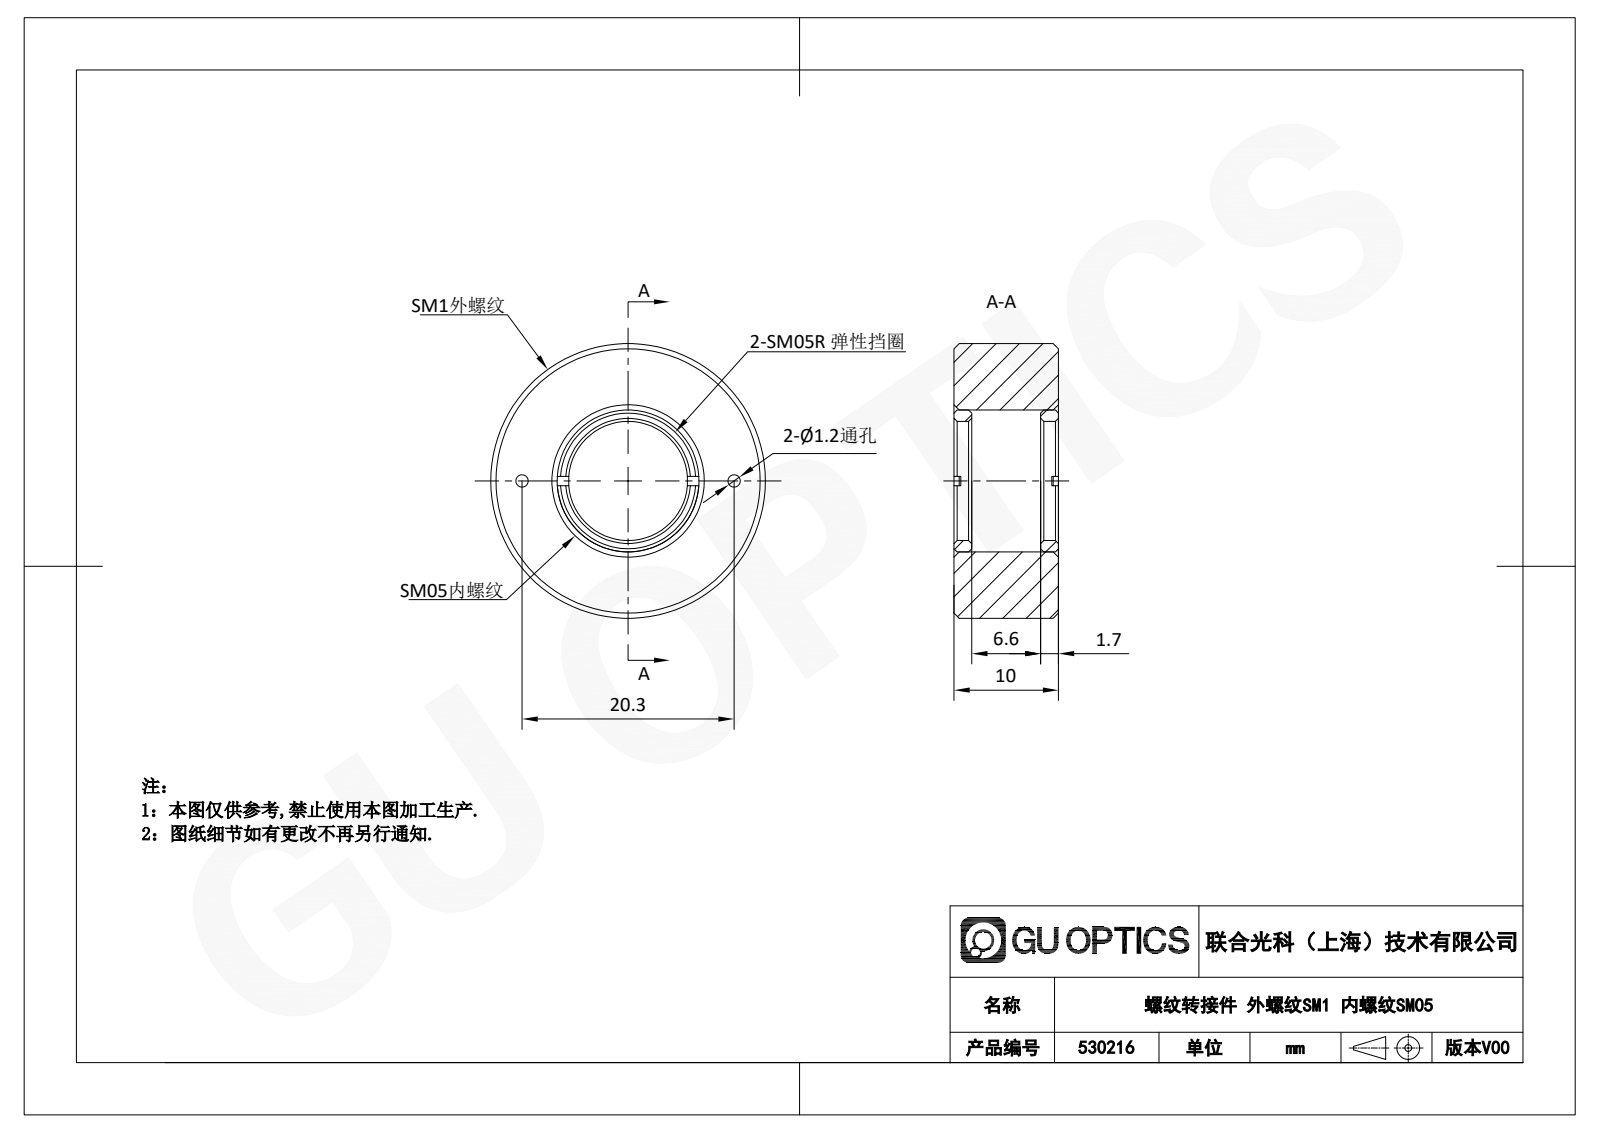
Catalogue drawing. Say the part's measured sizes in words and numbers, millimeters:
The part is named "SM1-SM05BT; 530216; SM05R". Its 3-D file was written by "SolidWorks 2020 (CONFIG_CONTROL_DESIGN)". It is 3 solids with 44 faces: 20 planar, 8 cylindrical and 16 other. Overall it measures 26.29 by 26.29 by 10 millimeters. Its volume is 4 054 cubic millimeters and its surface area 2 431 square millimeters. Round holes: 2 of diameter 1.2, 1 of diameter 11.4. Round bosses or shafts: 1 of diameter 26.29, 1 of diameter 13.59. The main face-to-face distances are 10, 1.7, 8.3, 6.6, 0.65, 9.35, 1.05, 7.65, 0.9, 8.7. The hole center spacings are 10.15, 20.3.
